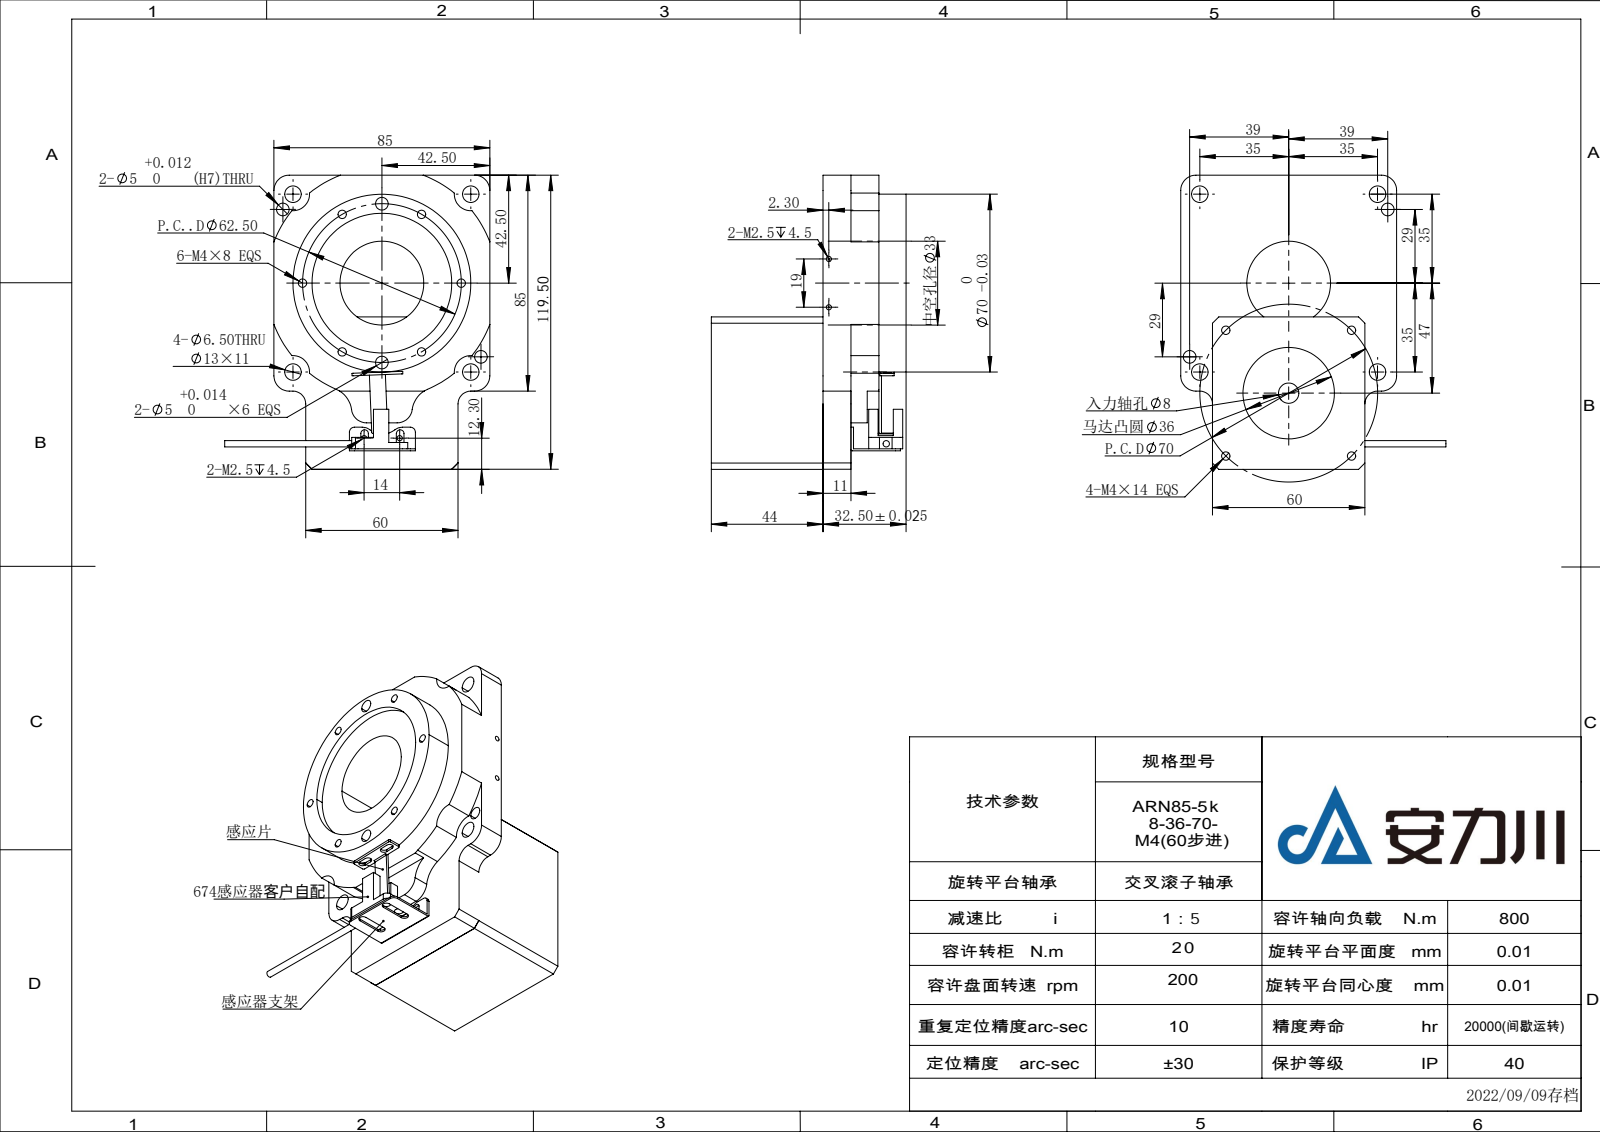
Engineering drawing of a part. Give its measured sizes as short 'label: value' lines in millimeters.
name: KTN85-5K-8-36-70-M4(60步进); SX674; 感应片1; 感应器支架
written by: SolidWorks 2020 (AUTOMOTIVE_DESIGN)
unit: mm
bodies: 4 solids, 278 faces (112 planar, 126 cylindrical, 40 other)
size: 119.5 × 104.62 × 76.5
volume: 330 357 mm³; area: 48 281 mm²
holes: 10× ⌀3.3, 6× ⌀2.05, 4× ⌀5, 4× ⌀6.5, 2× ⌀3.5, 1× ⌀8, 1× ⌀33, 1× ⌀36, 1× ⌀55
bosses: 1× ⌀70, 1× ⌀2.5
rounds: 9× R0.5, 8× R1.5, 6× R2, 6× R6, 4× R1.65, 4× R5, 4× R6.5, 2× R1
face distances: 60, 11, 44, 55, 22, 12.5, 66, 72.5, 29.7, 73.7
hole spacings: 31.25, 35.2, 49.5, 74.93, 70, 54.13, 35, 44.19
